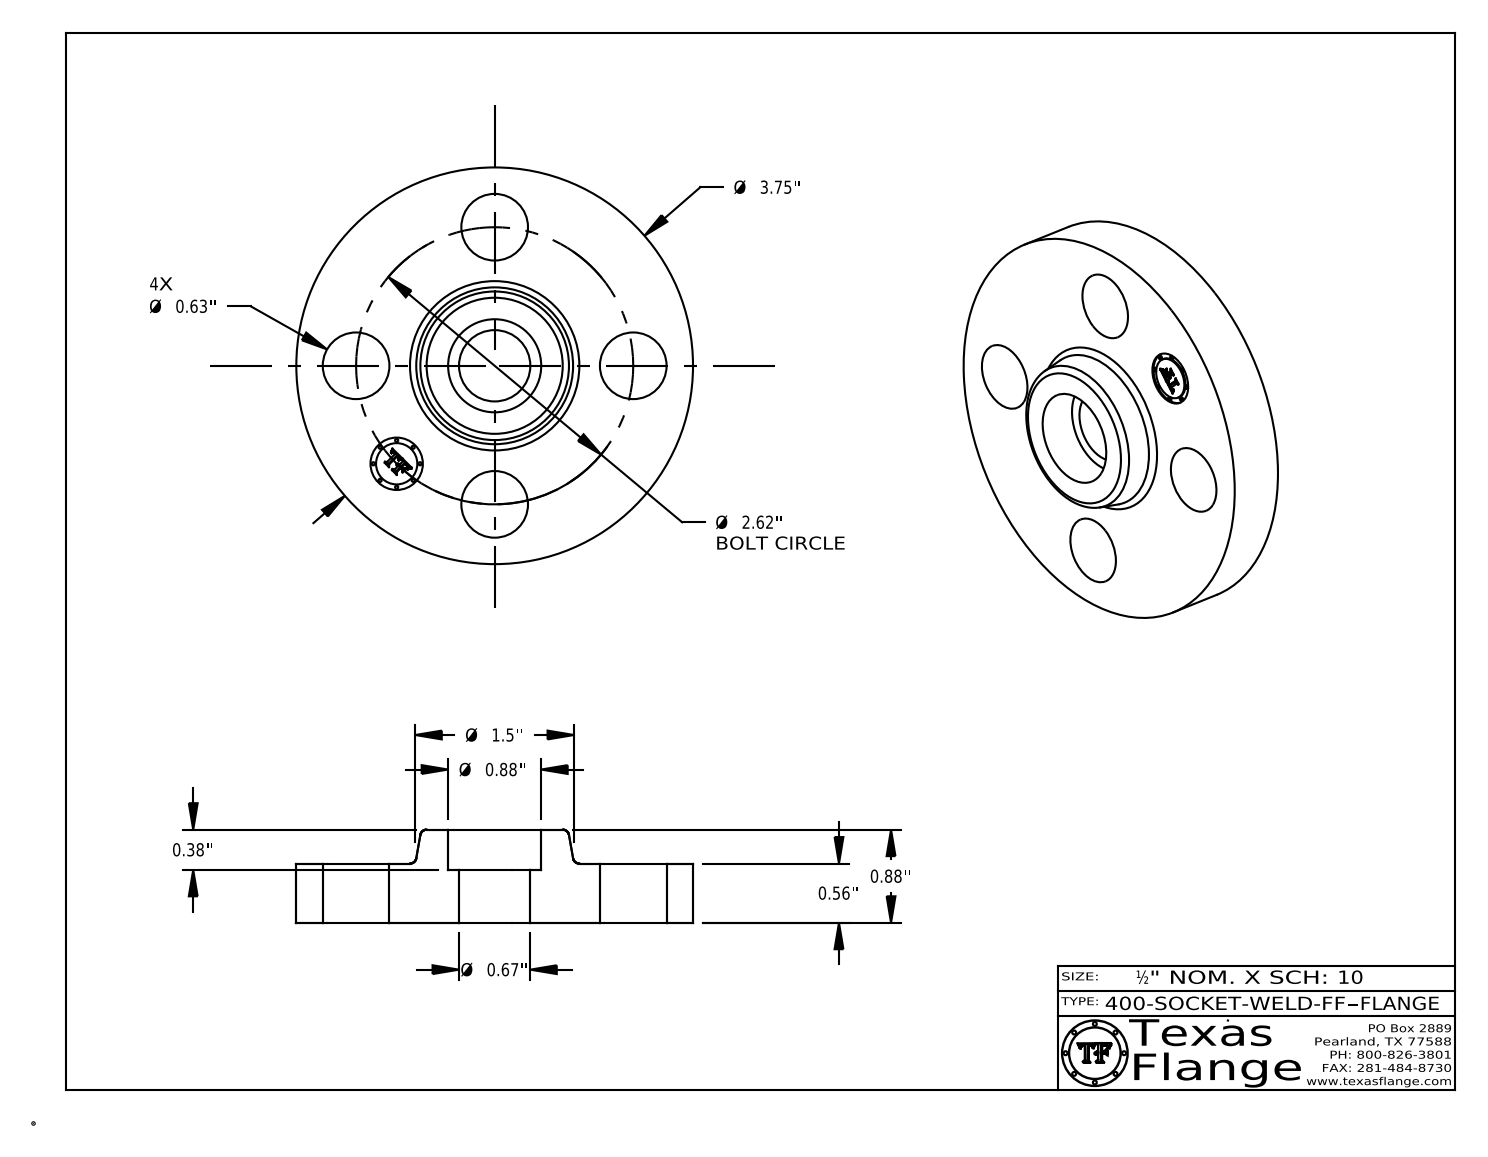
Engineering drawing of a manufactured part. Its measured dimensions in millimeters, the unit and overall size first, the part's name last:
Units: millimetres
Overall size (bounding box): 95.3 × 95.3 × 22.4
Round holes (diameter × count): ⌀16 ×4, ⌀12.6 ×1, ⌀17.1 ×1, ⌀22.4 ×1
Round bosses / shafts (diameter × count): ⌀0.8 ×8, ⌀95.3 ×1, ⌀9.9 ×1
Main face-to-face distances: 14.2, 22.4, 8.1, 12.7, 1.5, 9.7, 13.8, 1.1, 0.4, 8.5
Hole centre spacings: 33.3, 47, 25.5, 61.5, 66.5, 33.3
Volume: 91 770 mm³ · Surface area: 21 410 mm²
Bodies: 1 solid, 409 faces (369 planar, 34 cylindrical, 6 other)
Part name (STEP PRODUCT): 400-SOCKET-WELD-FF
STEP written by: CATIA V5 STEP AP214 (AUTOMOTIVE_DESIGN)
